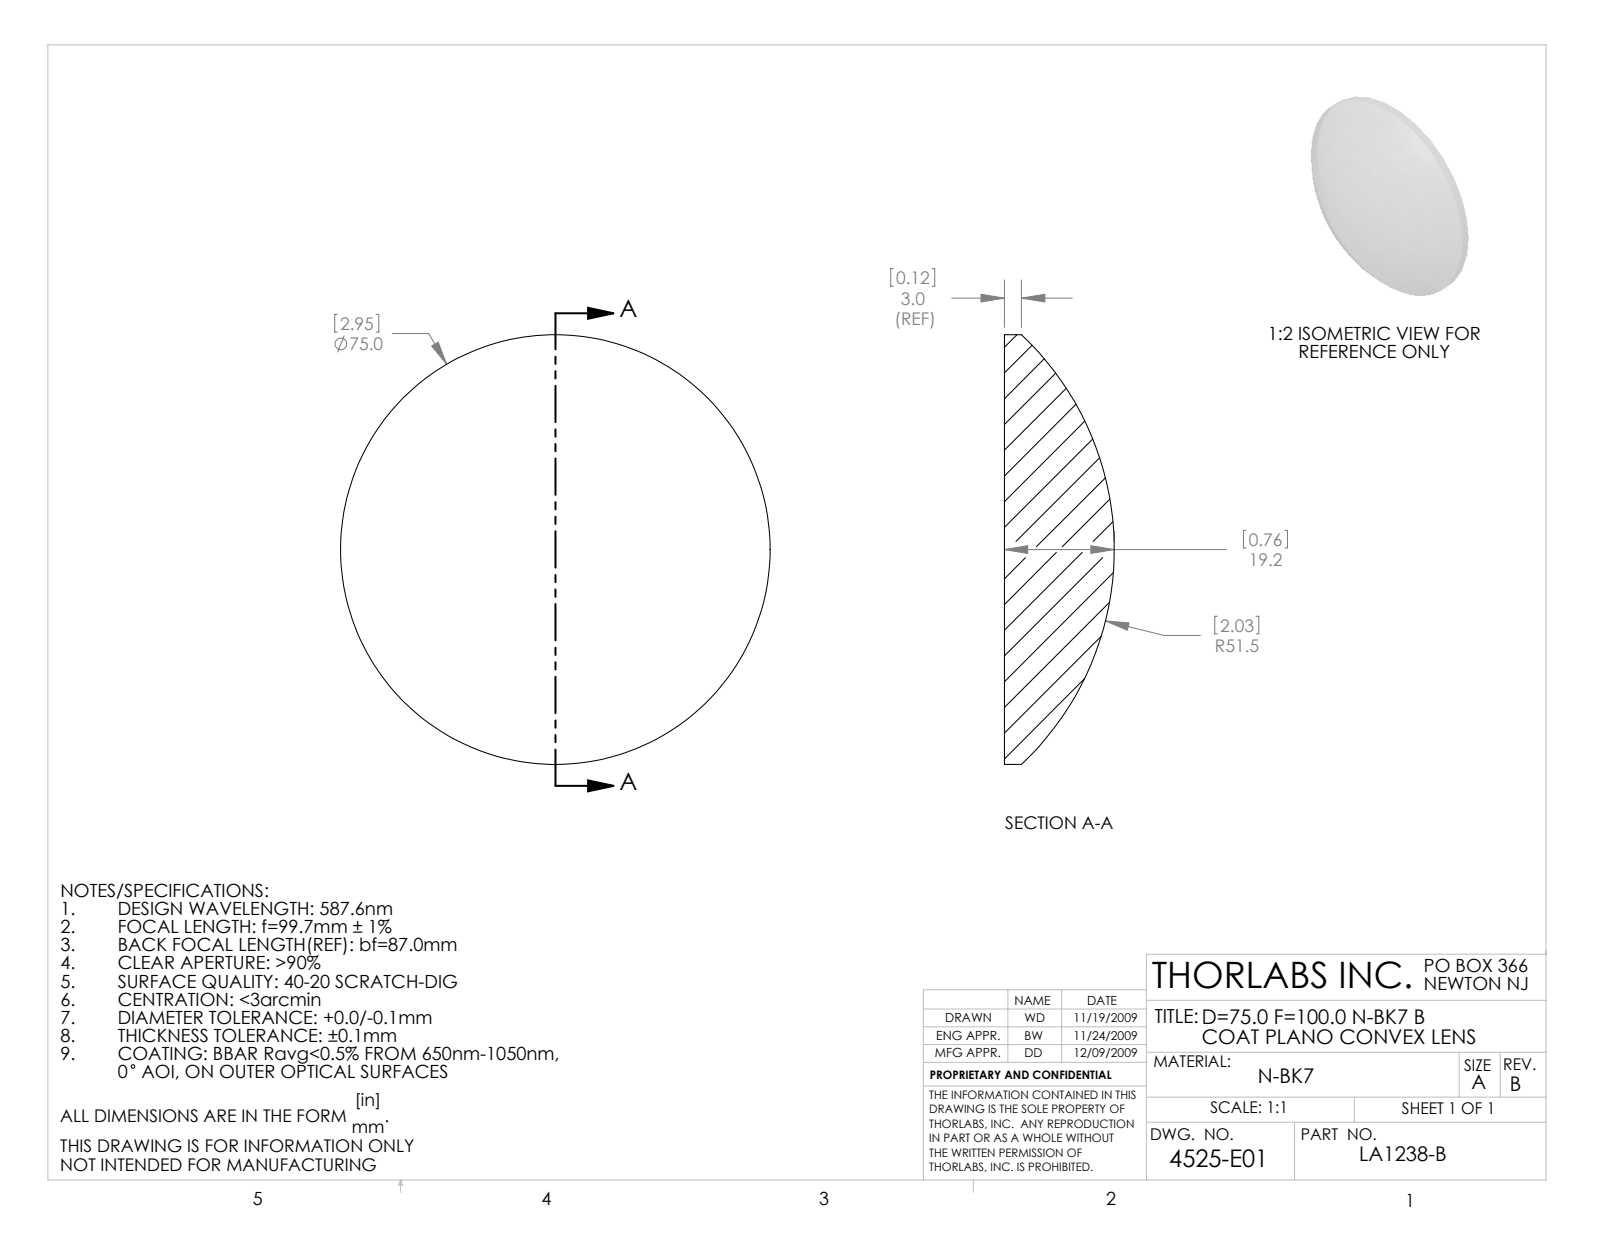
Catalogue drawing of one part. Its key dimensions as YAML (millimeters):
part_name: "4525-E0W"
step_written_by: "SolidWorks 2009 (AUTOMOTIVE_DESIGN)"
units: millimeters
bodies: {solids: 1, faces: 5, planar: 1, cylindrical: 2, other: 2}
overall_size: [75, 75, 19.19]
volume: 51218
surface_area: 10365
round_bosses_or_shafts:
  - {diameter: 75, count: 1}
